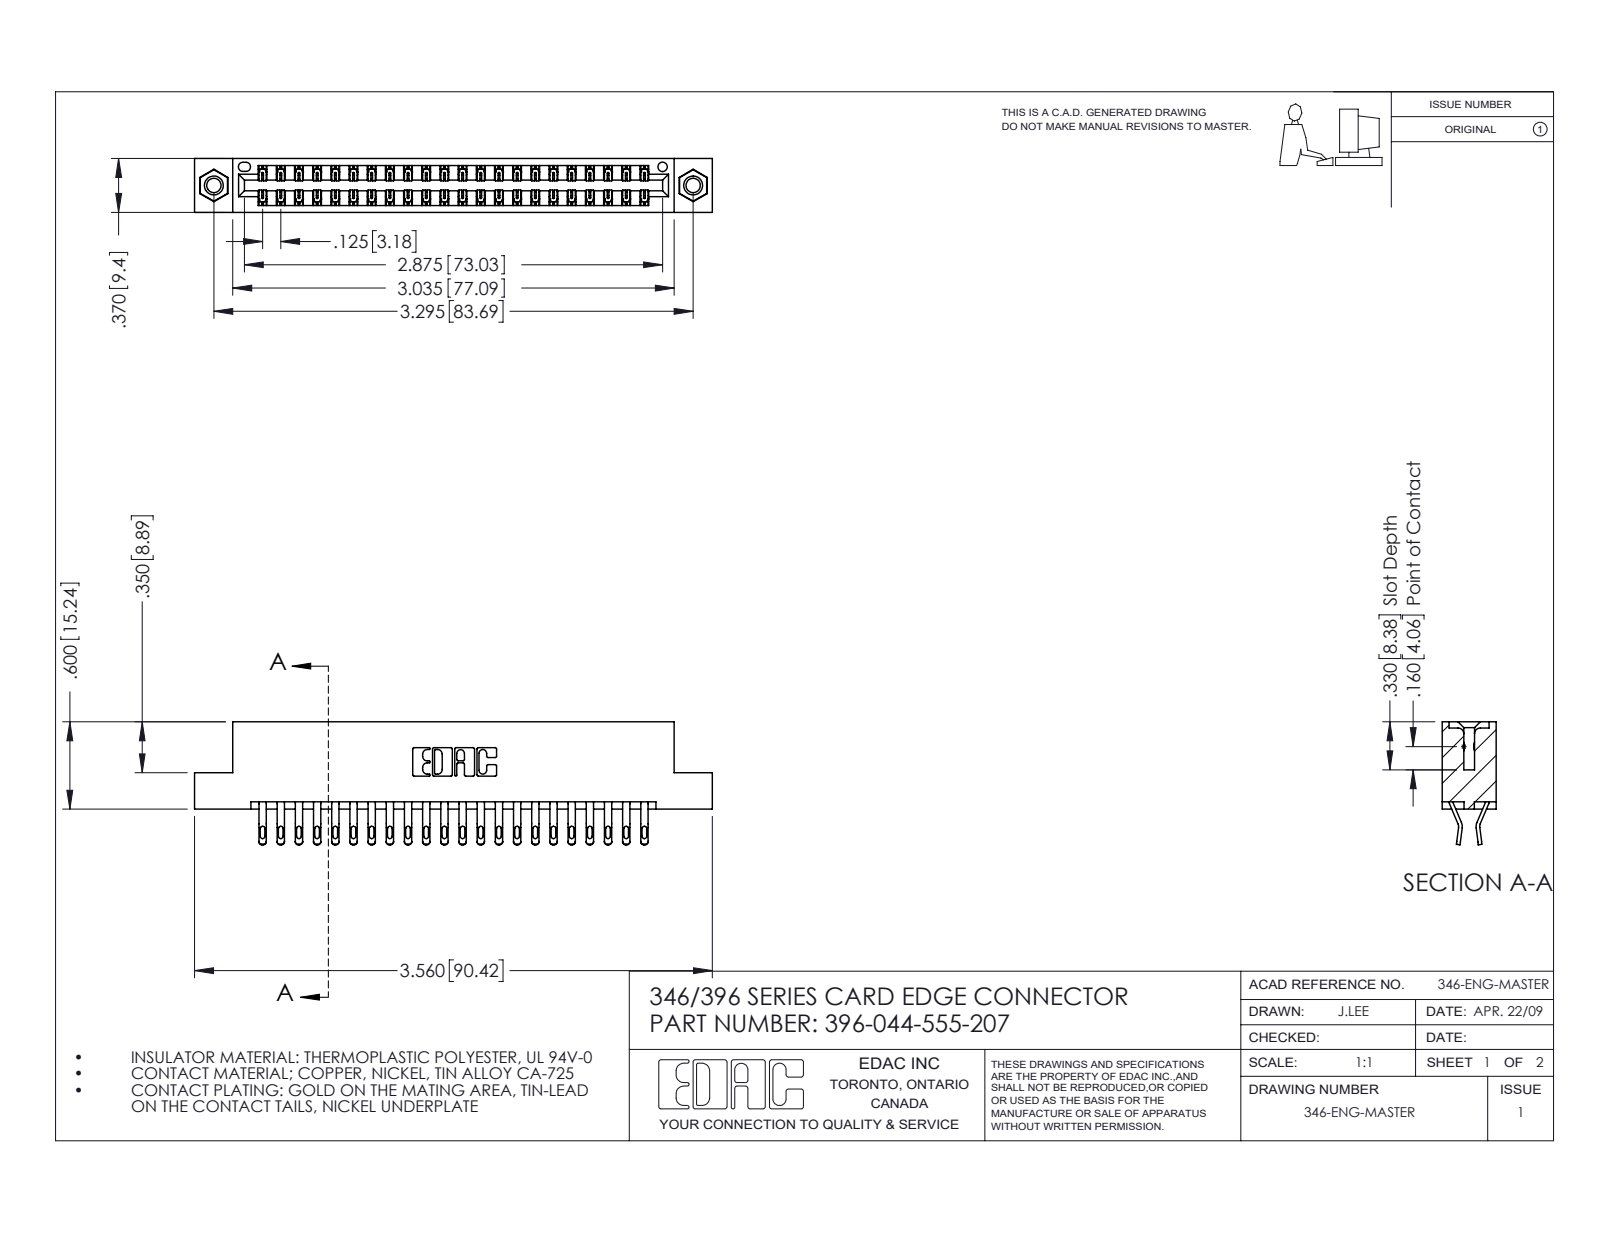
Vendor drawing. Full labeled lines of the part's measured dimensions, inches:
Part name (STEP PRODUCT): 345-292-001_555 Tail; 345-250-001_345-250-005-103; 396-044-555-207; 346 Part_Flush Mounting Lugs - 0.156 Dia-TI
STEP written by: SolidWorks 2016 (CONFIG_CONTROL_DESIGN)
Units: inches
Bodies: 47 solids, 2734 faces (1560 planar, 1158 cylindrical, 16 other)
Overall size (bounding box): 3.56 × 0.845 × 0.37
Volume: 0.536 in³ · Surface area: 18.97 in²
Round holes (diameter × count): ⌀0.098 ×2, ⌀0.125 ×2, ⌀0.156 ×2, ⌀0.064 ×1
Round bosses / shafts (diameter × count): ⌀0.155 ×2
Partial cylindrical surfaces — rounded edges, fillets, slot ends (radius × count): R0.016 ×88, R0.02 ×88, R0.006 ×66, R0.01 ×22, R0.007 ×6, R0.031 ×6, R0.026 ×3, R0.01 ×2
Main face-to-face distances: 0.048, 0.322, 0.25, 0.37, 0.025, 0.072, 0.298, 0.275, 0.148, 0.222
Hole centre spacings: 0.246, 3.087, 3.295
